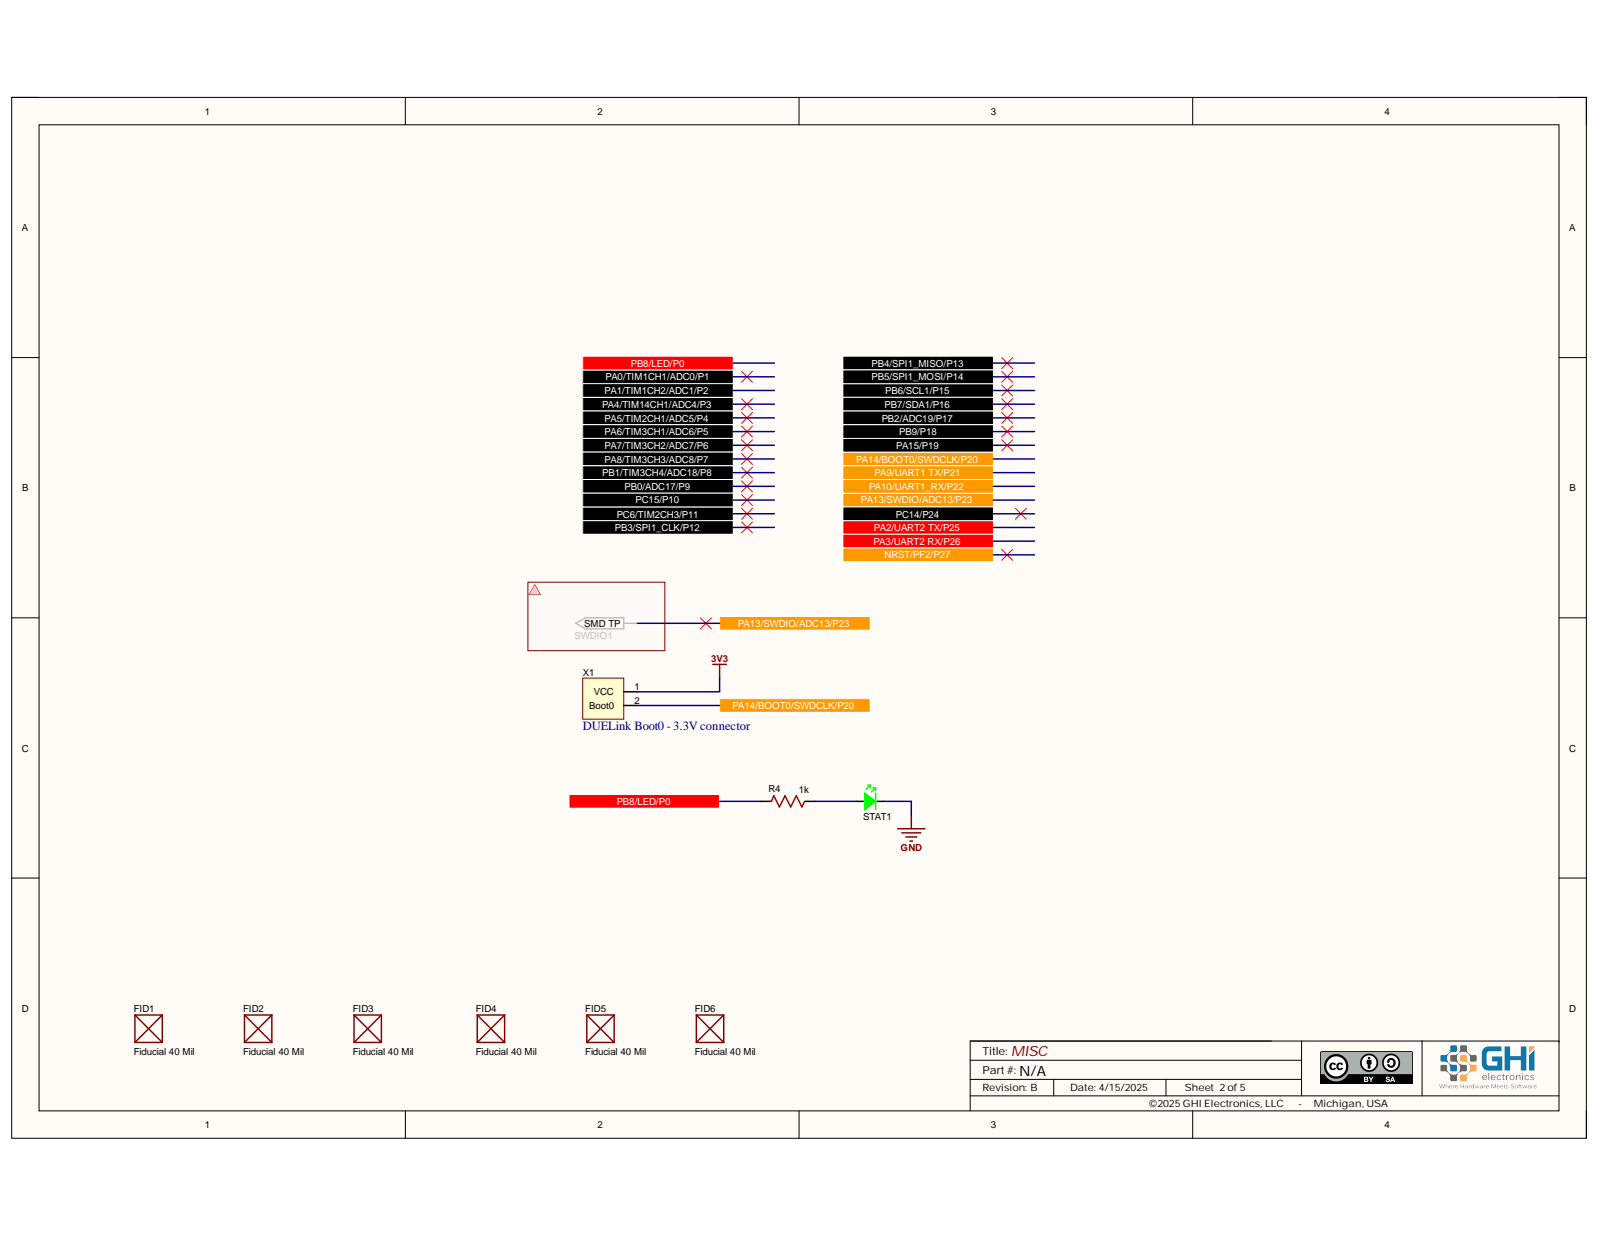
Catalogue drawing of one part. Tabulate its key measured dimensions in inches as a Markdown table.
| quantity | value |
| --- | --- |
| part name | PCB; Board; J12; Conn_Molex_90120-0763_eec (+3 more) |
| STEP written by | Open CASCADE 7.5 (AUTOMOTIVE_DESIGN) |
| units | inches |
| bodies | 100 solids, 1911 faces (1573 planar, 236 cylindrical, 102 other) |
| overall size | 1.416 × 1.024 × 0.669 |
| volume | 0.088 in³ |
| surface area | 4.326 in² |
| round holes (diameter × count) | 0.039 × 7, 0.04 × 2, 0.118 × 2 |
| round bosses / shafts (diameter × count) | 0.118 × 1 |
| partial cylindrical surfaces (radius × count) | 0.005 × 35, 0.006 × 14, 0.008 × 4, 0.004 × 2, 0.007 × 2, 0.007 × 2, 0.007 × 2, 0.012 × 2 |
| main face-to-face distances | 0.063, 0.811, 0.1, 0.874, 0.748, 0.197, 0.094, 0.026, 0.533, 0.022 |
| hole center spacings | 0.1, 0.221, 0.394, 0.406, 0.172, 0.196, 0.197, 0.2 |
